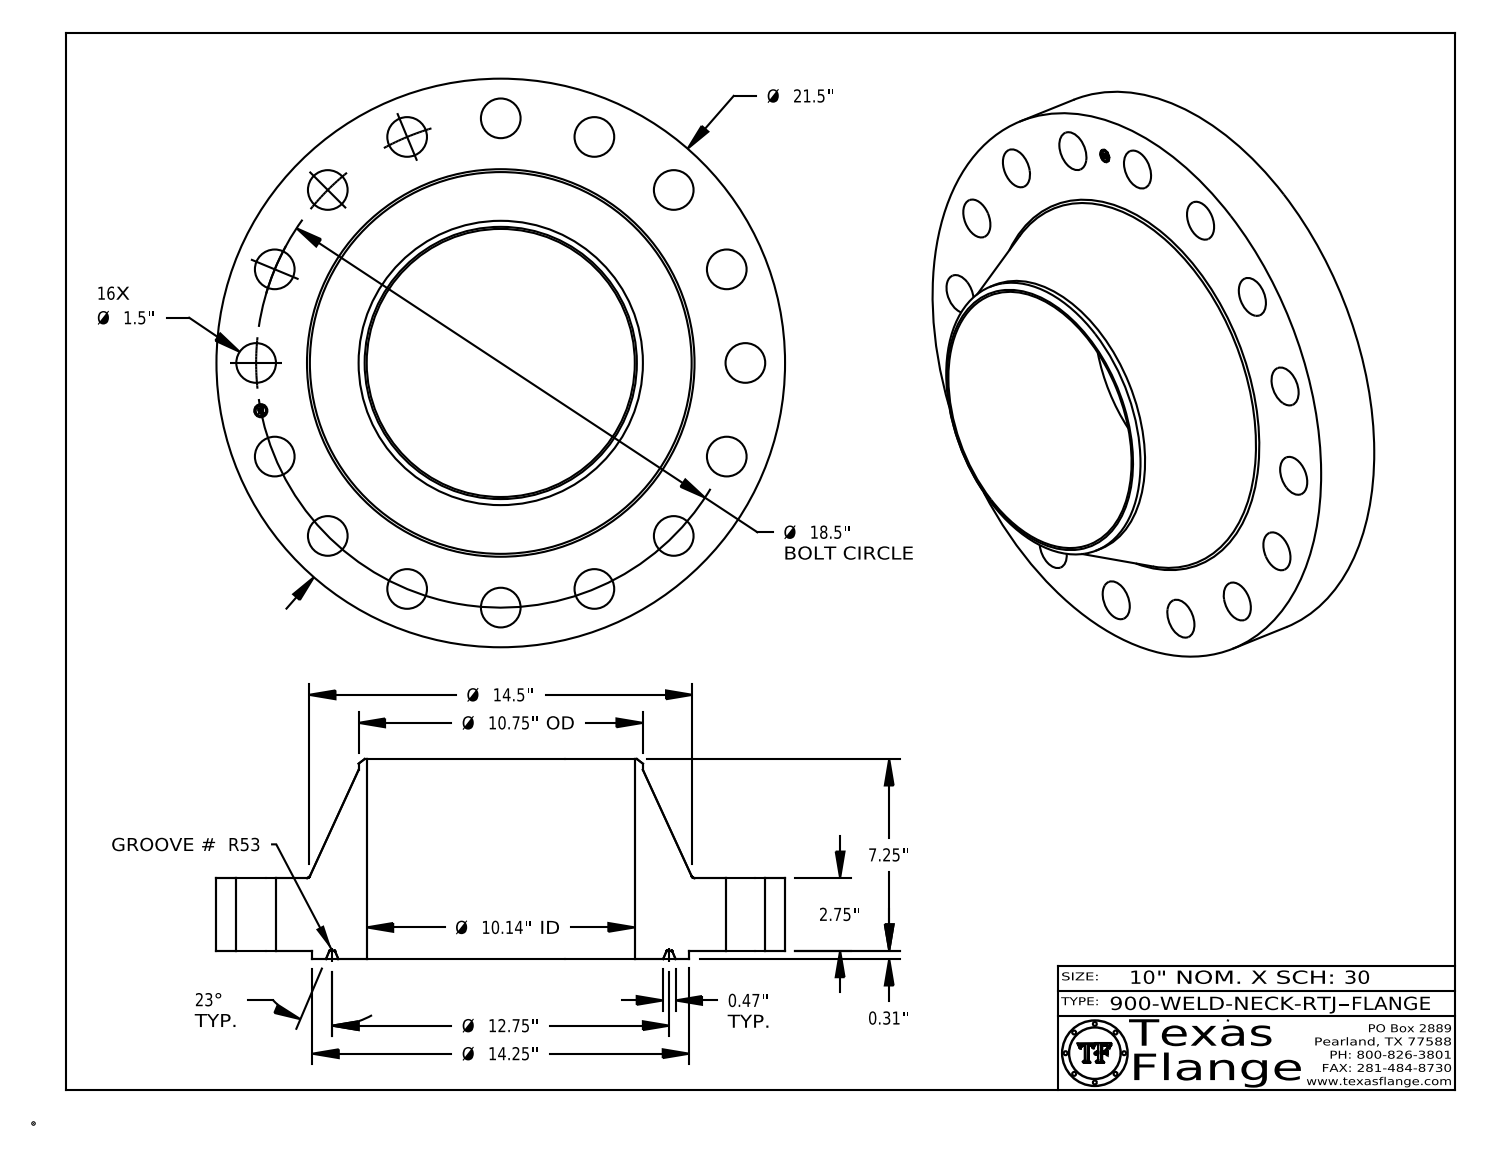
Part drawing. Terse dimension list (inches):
name: 900-WELD-NECK-RTJ
written by: CATIA V5 STEP AP214 (AUTOMOTIVE_DESIGN)
unit: in
bodies: 1 solid, 445 faces (371 planar, 60 cylindrical, 14 other)
size: 21.5 × 21.5 × 7.563
volume: 908.4 in³; area: 1 286 in²
holes: 16× ⌀1.5, 1× ⌀0.495, 1× ⌀10.136
bosses: 8× ⌀0.03, 1× ⌀21.5, 1× ⌀14.25, 1× ⌀10.75, 1× ⌀0.39
face distances: 2.75, 0.313, 3.063, 7.563, 7.25, 4.5, 3.048, 2.735, 0.015, 4.515
hole spacings: 15.382, 7.08, 9.25, 13.081, 3.609, 3.609, 10.278, 10.278
